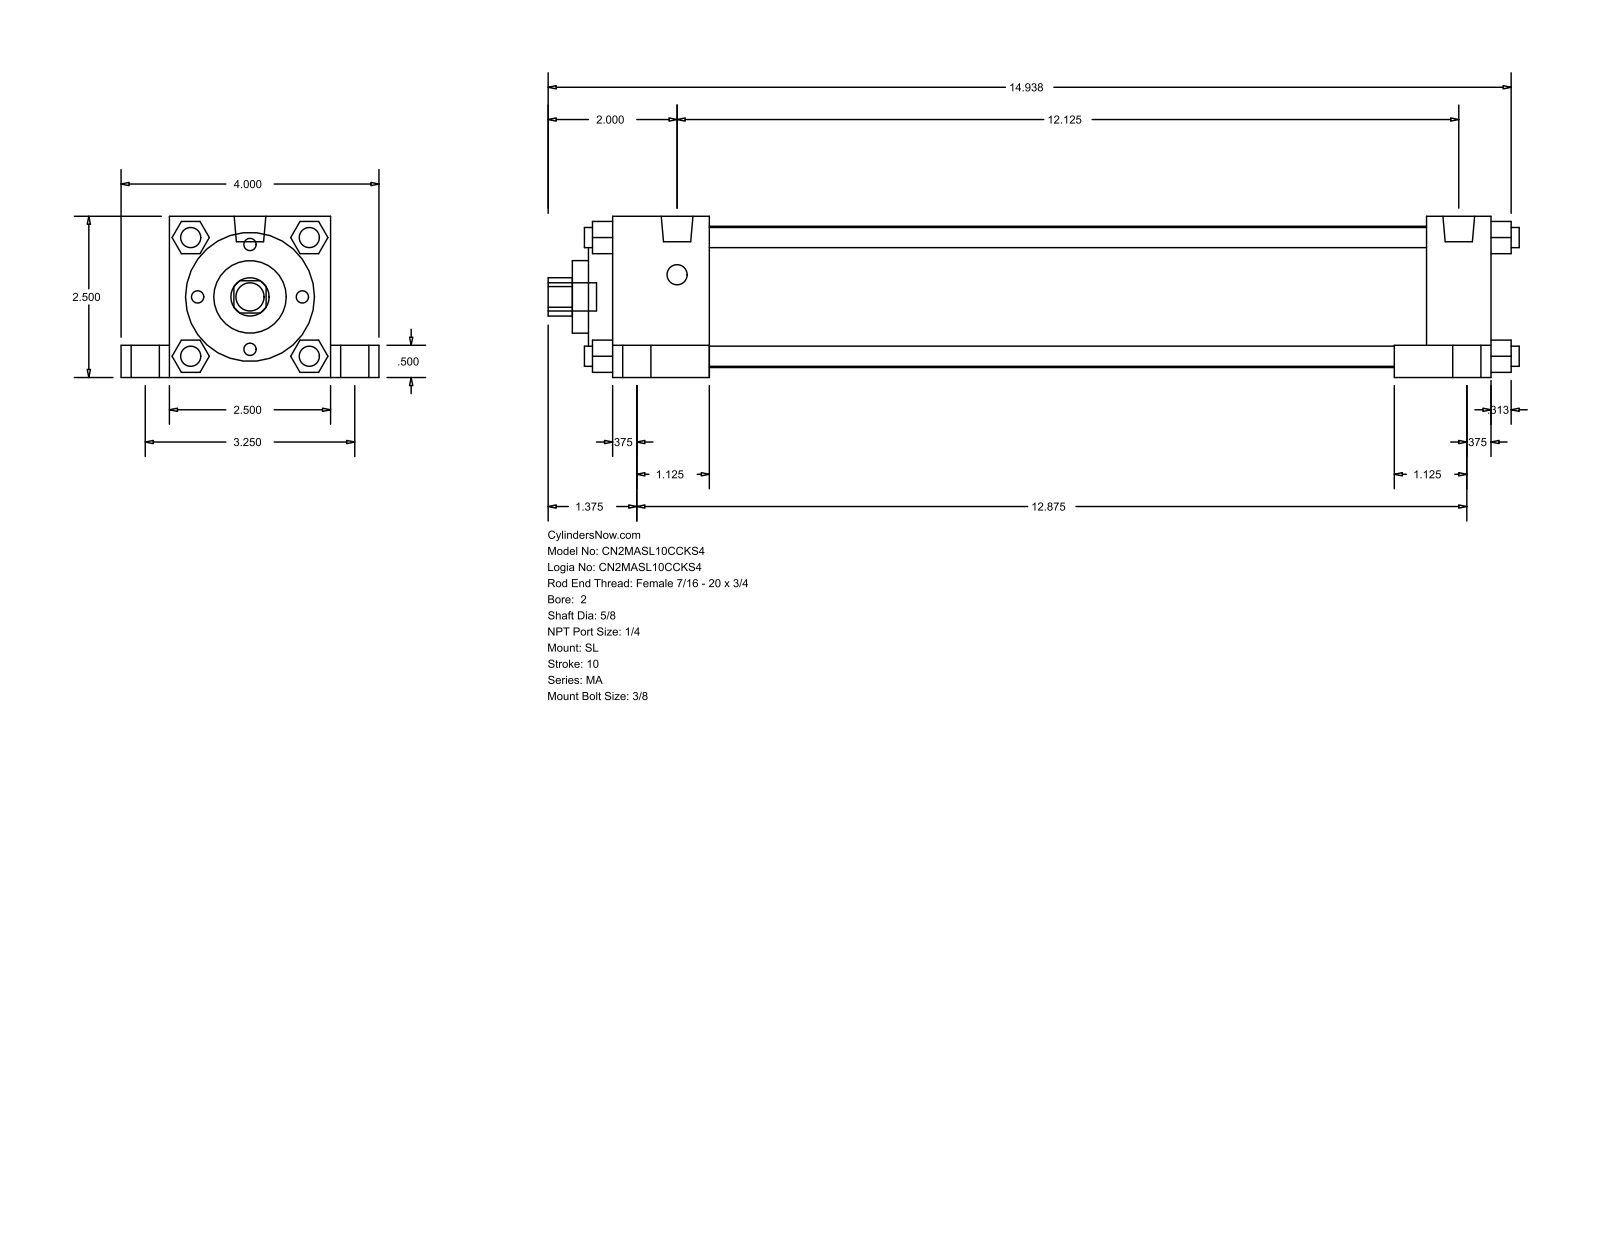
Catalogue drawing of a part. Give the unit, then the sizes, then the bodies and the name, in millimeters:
Units: millimetres
Overall size (bounding box): 382.59 × 101.6 × 63.5
Round holes (diameter × count): ⌀15.88 ×1, ⌀28.57 ×1, ⌀50.8 ×1, ⌀55.63 ×1
Round bosses / shafts (diameter × count): ⌀7.94 ×8, ⌀11.11 ×5, ⌀17.46 ×4, ⌀12.49 ×2
Partial cylindrical surfaces — rounded edges, fillets, slot ends (radius × count): R7.54 ×1
Main face-to-face distances: 63.5, 12.7, 9.52, 282.57, 19.05, 82.55, 38.1, 50.8, 346.08, 307.98
Bodies: 0 solids, 150 faces (113 planar, 37 cylindrical, 0 other)
Part name (STEP PRODUCT): MA_SL__0200_0.625
STEP written by: GSSL Pune (CONFIG_CONTROL_DESIGN)
